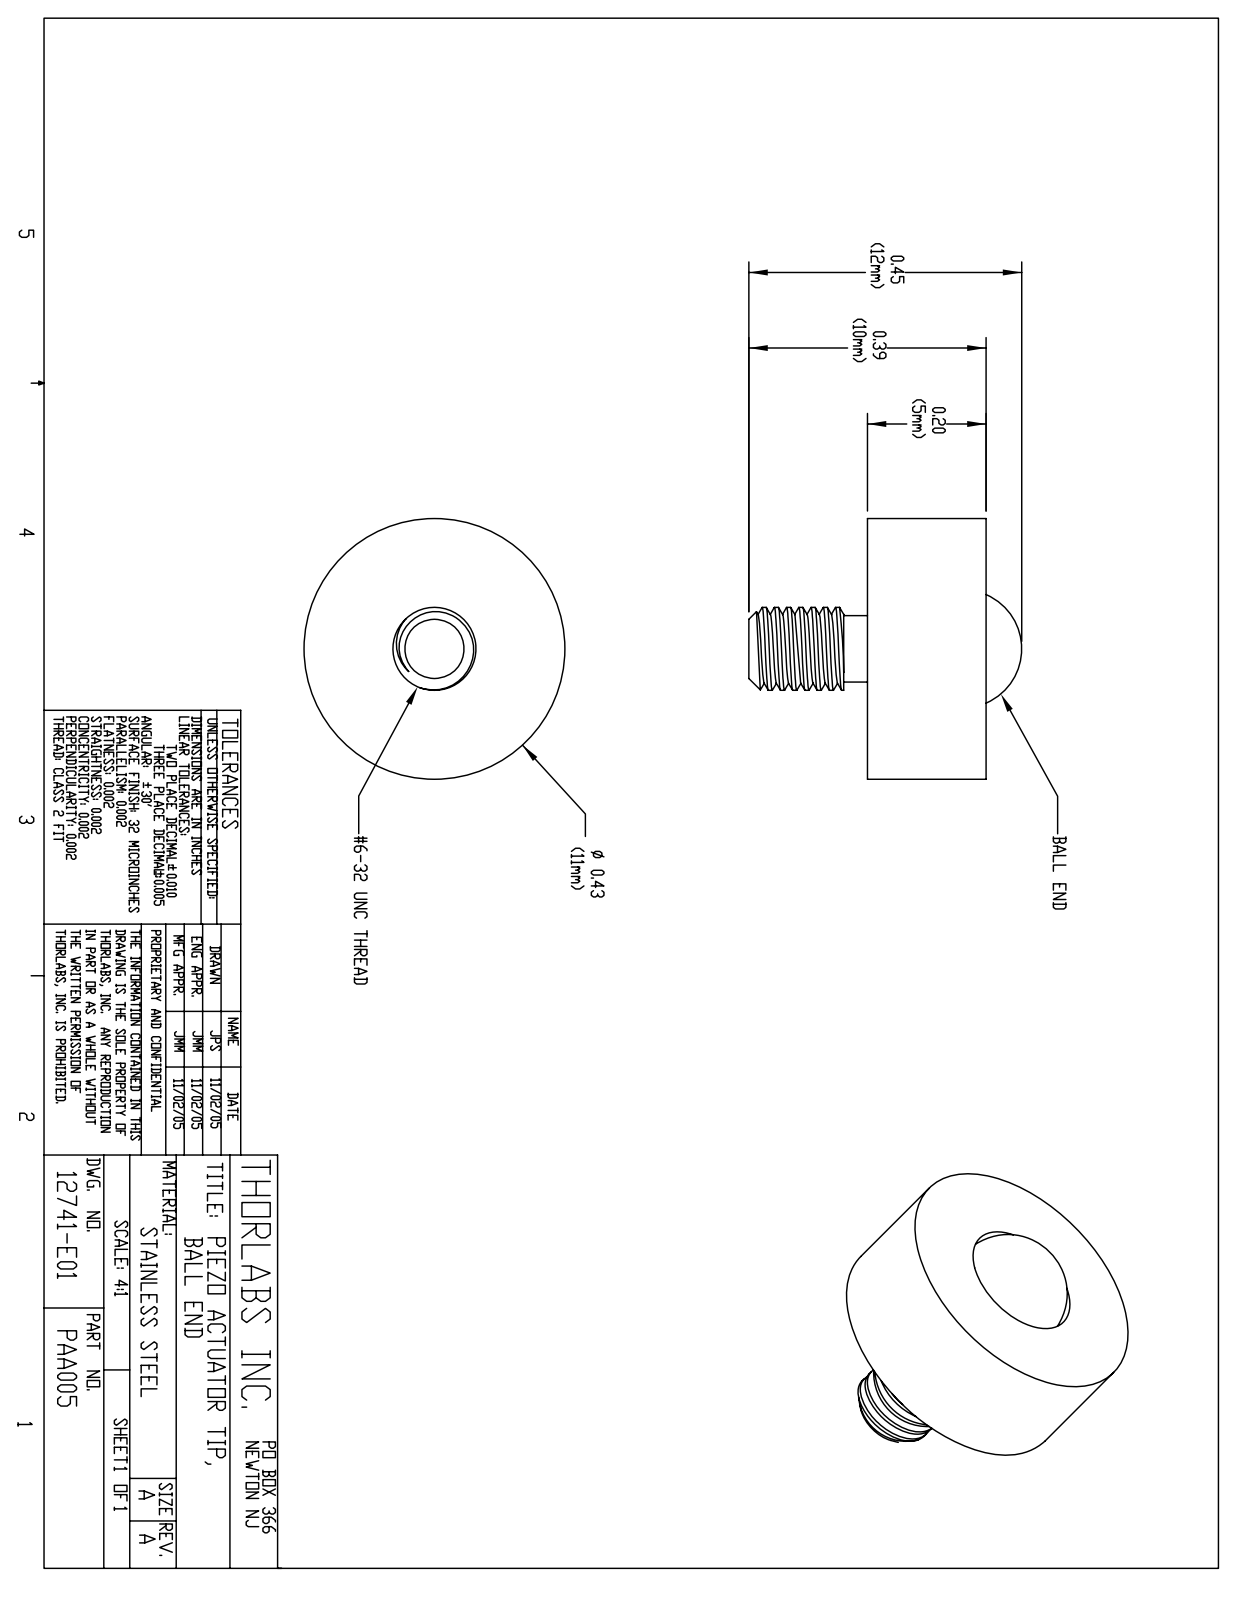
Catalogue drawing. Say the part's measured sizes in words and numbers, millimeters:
The part is named "12741-E0W". Its 3-D file was written by "SolidWorks 2007 (AUTOMOTIVE_DESIGN)". It is 0 solids with 30 faces: 3 planar, 21 cylindrical and 6 other. Overall it measures 11.5 by 11 by 11 millimeters. Round holes: 1 of diameter 5. Round bosses or shafts: 1 of diameter 11, 1 of diameter 3.5, 1 of diameter 2.8. The main face-to-face distances are 5, 10.
